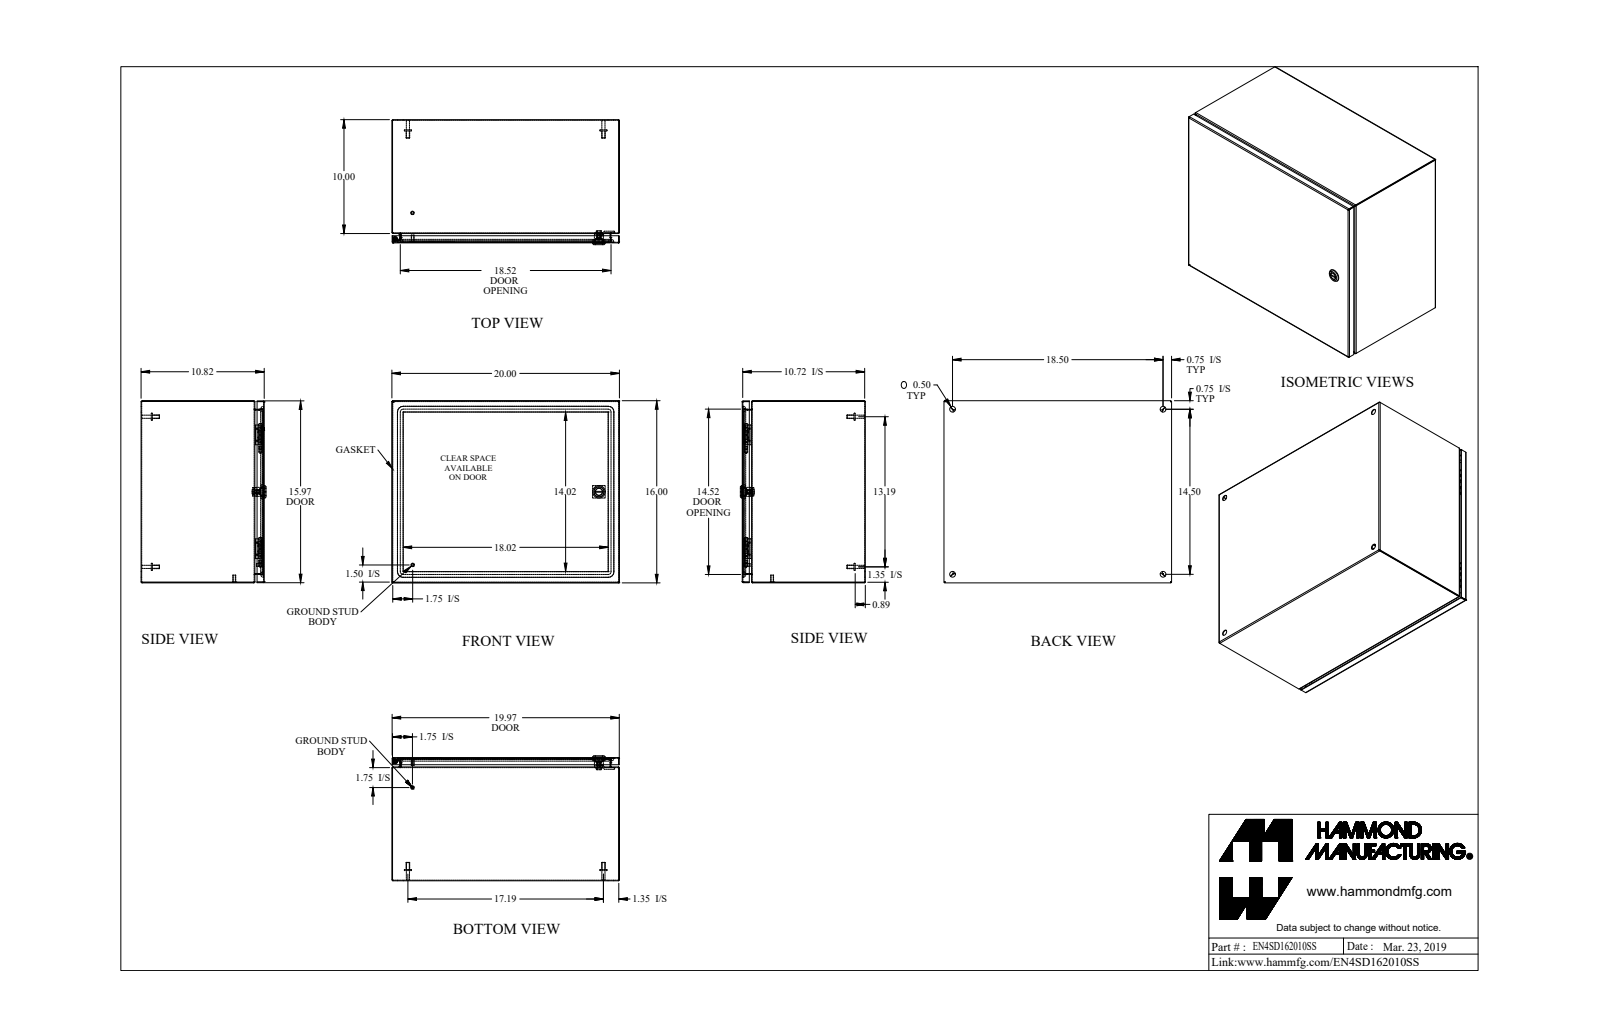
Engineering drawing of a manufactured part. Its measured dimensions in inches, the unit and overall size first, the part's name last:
Units: inches
Overall size (bounding box): 20 × 16 × 10.982
Round holes (diameter × count): ⌀0.5 ×5, ⌀0.172 ×1, ⌀0.197 ×1, ⌀0.24 ×1, ⌀0.242 ×1, ⌀0.387 ×1, ⌀0.63 ×1, ⌀0.768 ×1
Round bosses / shafts (diameter × count): ⌀0.313 ×6, ⌀0.625 ×5, ⌀0.275 ×4, ⌀0.25 ×2, ⌀1.1 ×1, ⌀0.785 ×1, ⌀0.525 ×1, ⌀0.455 ×1
Partial cylindrical surfaces — rounded edges, fillets, slot ends (radius × count): R0.029 ×21, R0.086 ×21, R0.188 ×12, R0.006 ×4, R0.062 ×4, R0.25 ×4, R0.499 ×4, R0.125 ×2
Main face-to-face distances: 0.057, 10.765, 15.943, 10.708, 10.822, 19.943, 15.886, 16, 19.886, 20
Hole centre spacings: 7.327, 14.5, 18.5, 18.888, 23.506
Volume: 92.62 in³ · Surface area: 3 162 in²
Bodies: 22 solids, 657 faces (303 planar, 212 cylindrical, 142 other)
Part name (STEP PRODUCT): EN4SD162010SS_Default
STEP written by: SolidWorks 2019 (CONFIG_CONTROL_DESIGN)
